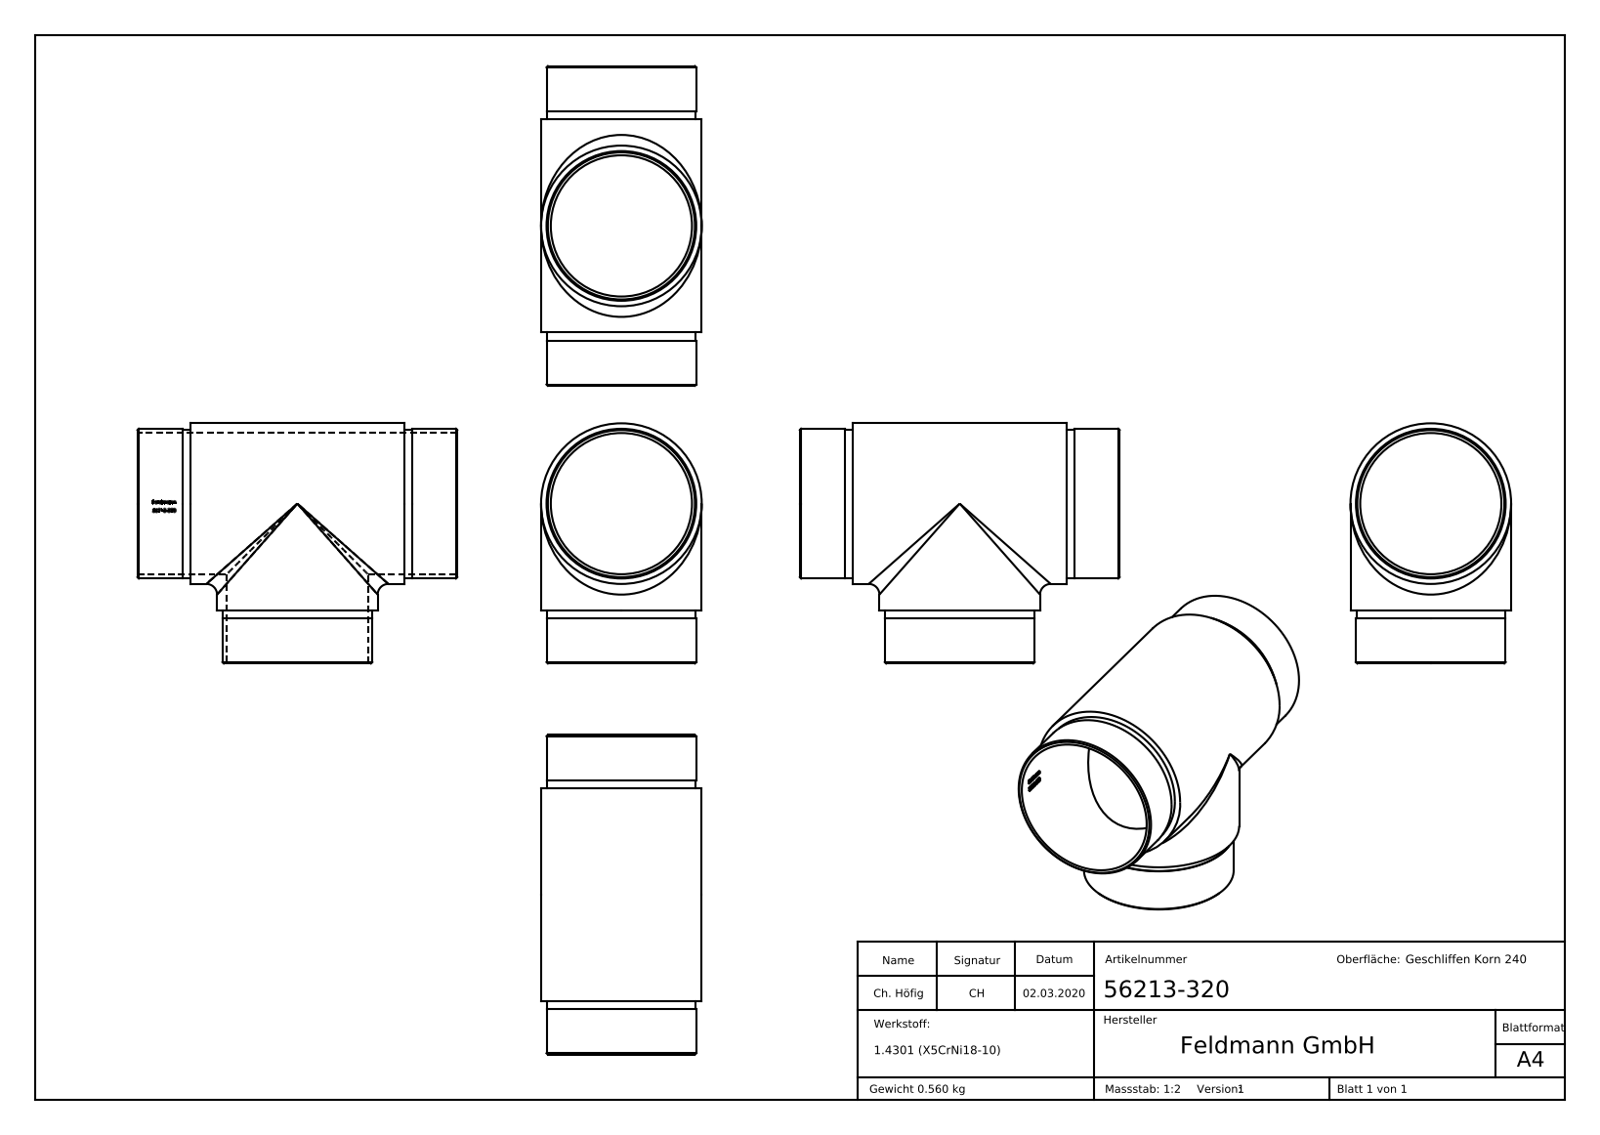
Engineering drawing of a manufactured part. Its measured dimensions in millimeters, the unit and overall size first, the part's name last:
Units: millimetres
Overall size (bounding box): 120 × 90.15 × 60.3
Round holes (diameter × count): ⌀53 ×2
Round bosses / shafts (diameter × count): ⌀60.3 ×2, ⌀56.2 ×2, ⌀55.8 ×2
Partial cylindrical surfaces — rounded edges, fillets, slot ends (radius × count): R26.6 ×1
Main face-to-face distances: 20, 80, 100, 120, 17, 3, 103, 83, 86, 3.53
Volume: 70 836 mm³ · Surface area: 52 288 mm²
Bodies: 1 solid, 251 faces (100 planar, 32 cylindrical, 119 other)
Part name (STEP PRODUCT): 56213-320
STEP written by: SolidWorks 2015 (CONFIG_CONTROL_DESIGN)
